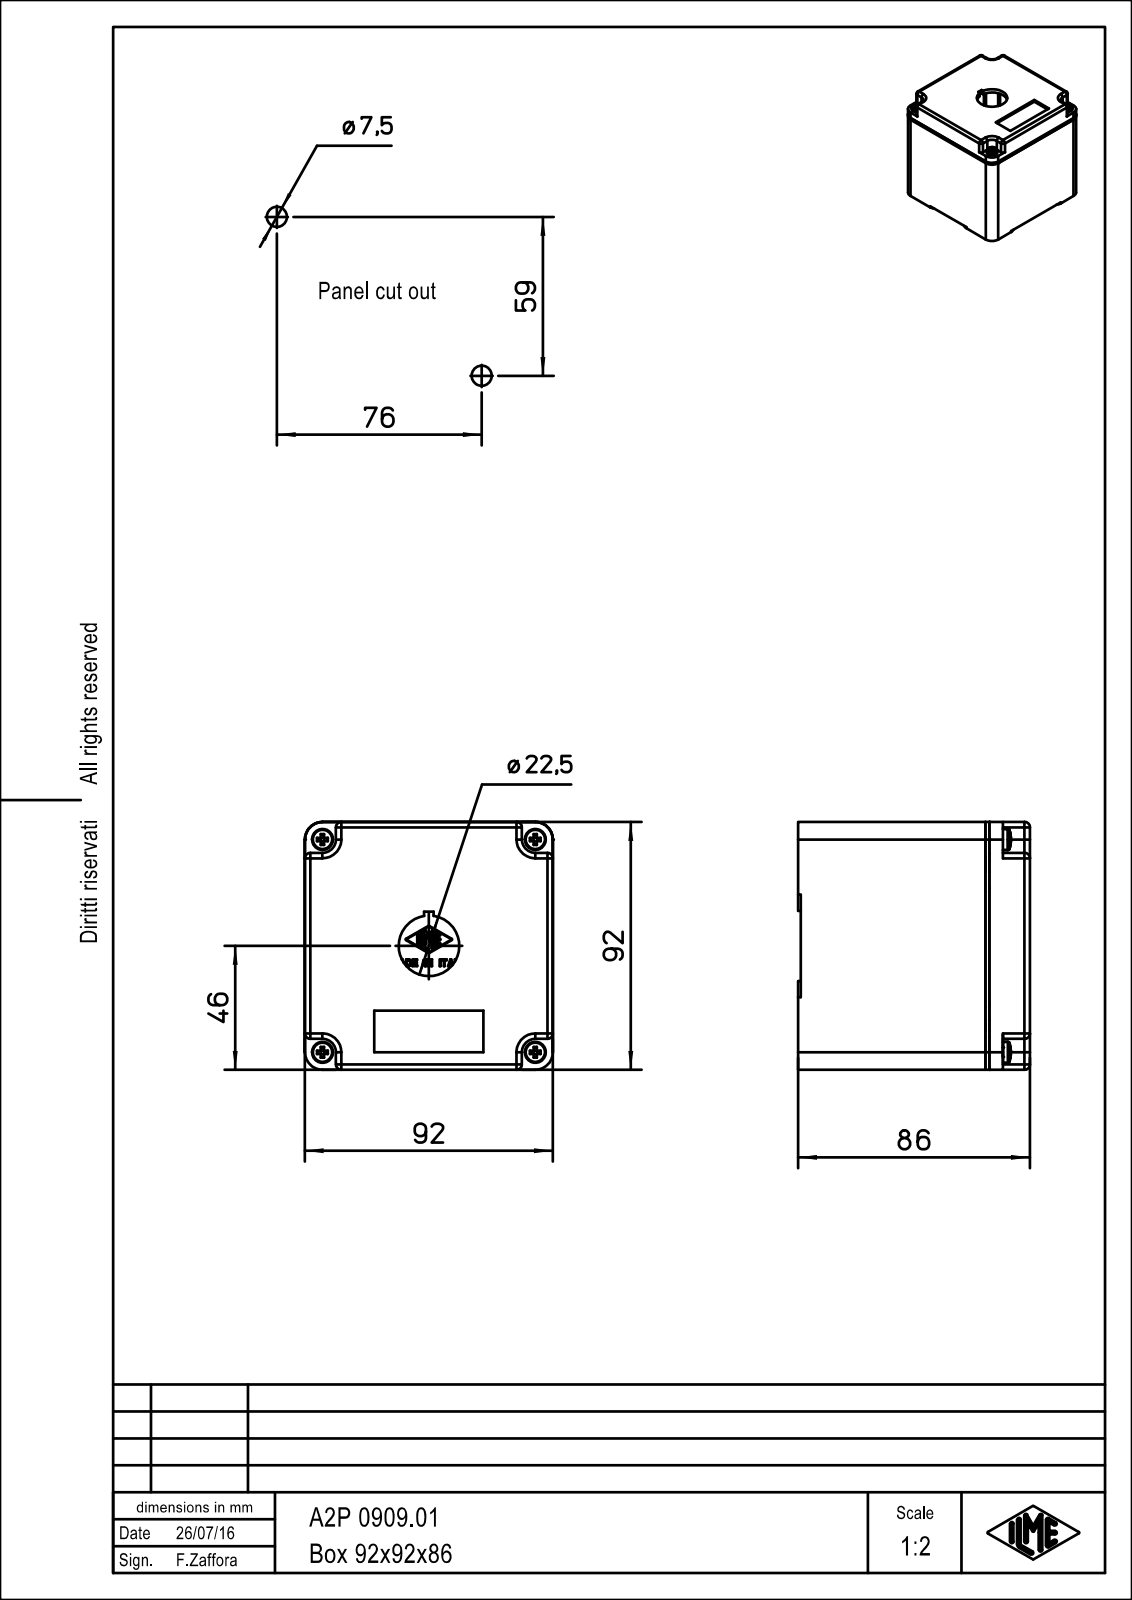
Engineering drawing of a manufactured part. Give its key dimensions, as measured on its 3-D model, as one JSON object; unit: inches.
{"part_name": "COVER; BOX; A2P_0909.01", "step_written_by": "PTC Creo Elements/Direct Modeling 19.0B 21-Mar-2015 (C) Parametric Technology GmbH (AUTOMOTIVE_DESIGN)", "units": "inches", "bodies": {"solids": 2, "faces": 1000, "planar": 790, "cylindrical": 170, "other": 40}, "overall_size": [3.623, 3.622, 3.386], "volume_in3": 13.5, "surface_area_in2": 159.7, "round_holes": [[0.13, 6], [0.177, 4], [0.228, 2], [0.295, 2], [0.417, 2], [0.886, 1]], "round_bosses_or_shafts": [[0.307, 4], [0.157, 4], [0.244, 2], [0.236, 2], [0.276, 1]], "partial_cylinders_radius": [[0.013, 22], [0.079, 17], [0.236, 12], [0.256, 12], [0.197, 6], [0.315, 6], [0.011, 4], [0.011, 4]], "face_to_face_distances": [0.118, 3.622, 3.228, 0.172, 3.45, 3.45, 0.172, 3.278, 0.531, 2.579], "hole_center_spacings": [3.11, 4.398, 2.199, 3.076, 4.085, 0.398, 0.459, 0.463]}
